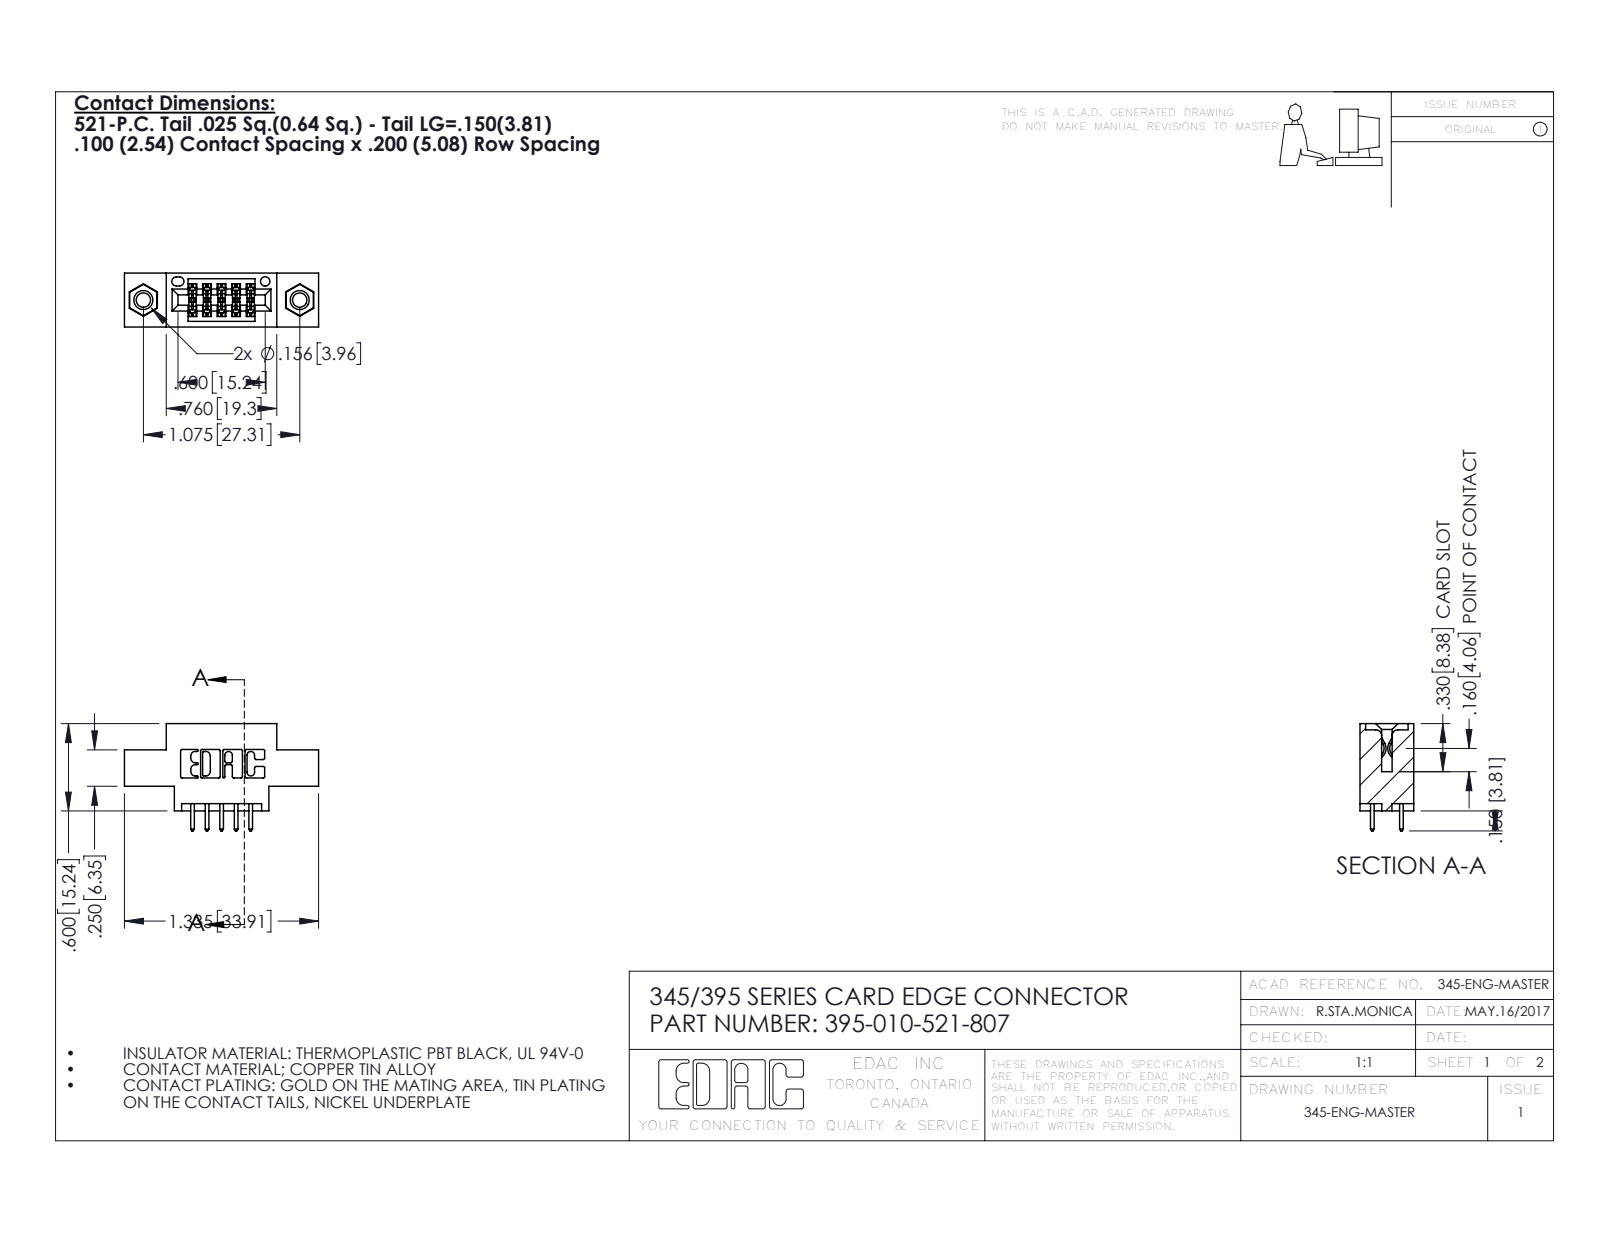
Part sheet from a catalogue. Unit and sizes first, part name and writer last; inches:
Units: inches
Overall size (bounding box): 1.335 × 0.737 × 0.37
Round holes (diameter × count): ⌀0.098 ×2, ⌀0.125 ×2, ⌀0.156 ×2, ⌀0.064 ×1
Round bosses / shafts (diameter × count): ⌀0.155 ×2
Partial cylindrical surfaces — rounded edges, fillets, slot ends (radius × count): R0.01 ×22, R0.006 ×15, R0.01 ×10, R0.007 ×6, R0.031 ×6, R0.026 ×3, R0.014 ×2, R0.019 ×2
Main face-to-face distances: 0.37, 0.2, 0.072, 0.298, 0.1, 0.025, 0.098, 0.272, 0.25, 0.225
Hole centre spacings: 0.27, 0.847, 1.075
Volume: 0.172 in³ · Surface area: 5.574 in²
Bodies: 13 solids, 690 faces (446 planar, 228 cylindrical, 16 other)
Part name (STEP PRODUCT): 395-010-521-807; 345 Part_0.170 Offset - 0.156 Dia-TI; 345-250-001_345-250-005-103; 345-292-001_345-293-121
STEP written by: SolidWorks 2016 (CONFIG_CONTROL_DESIGN)
